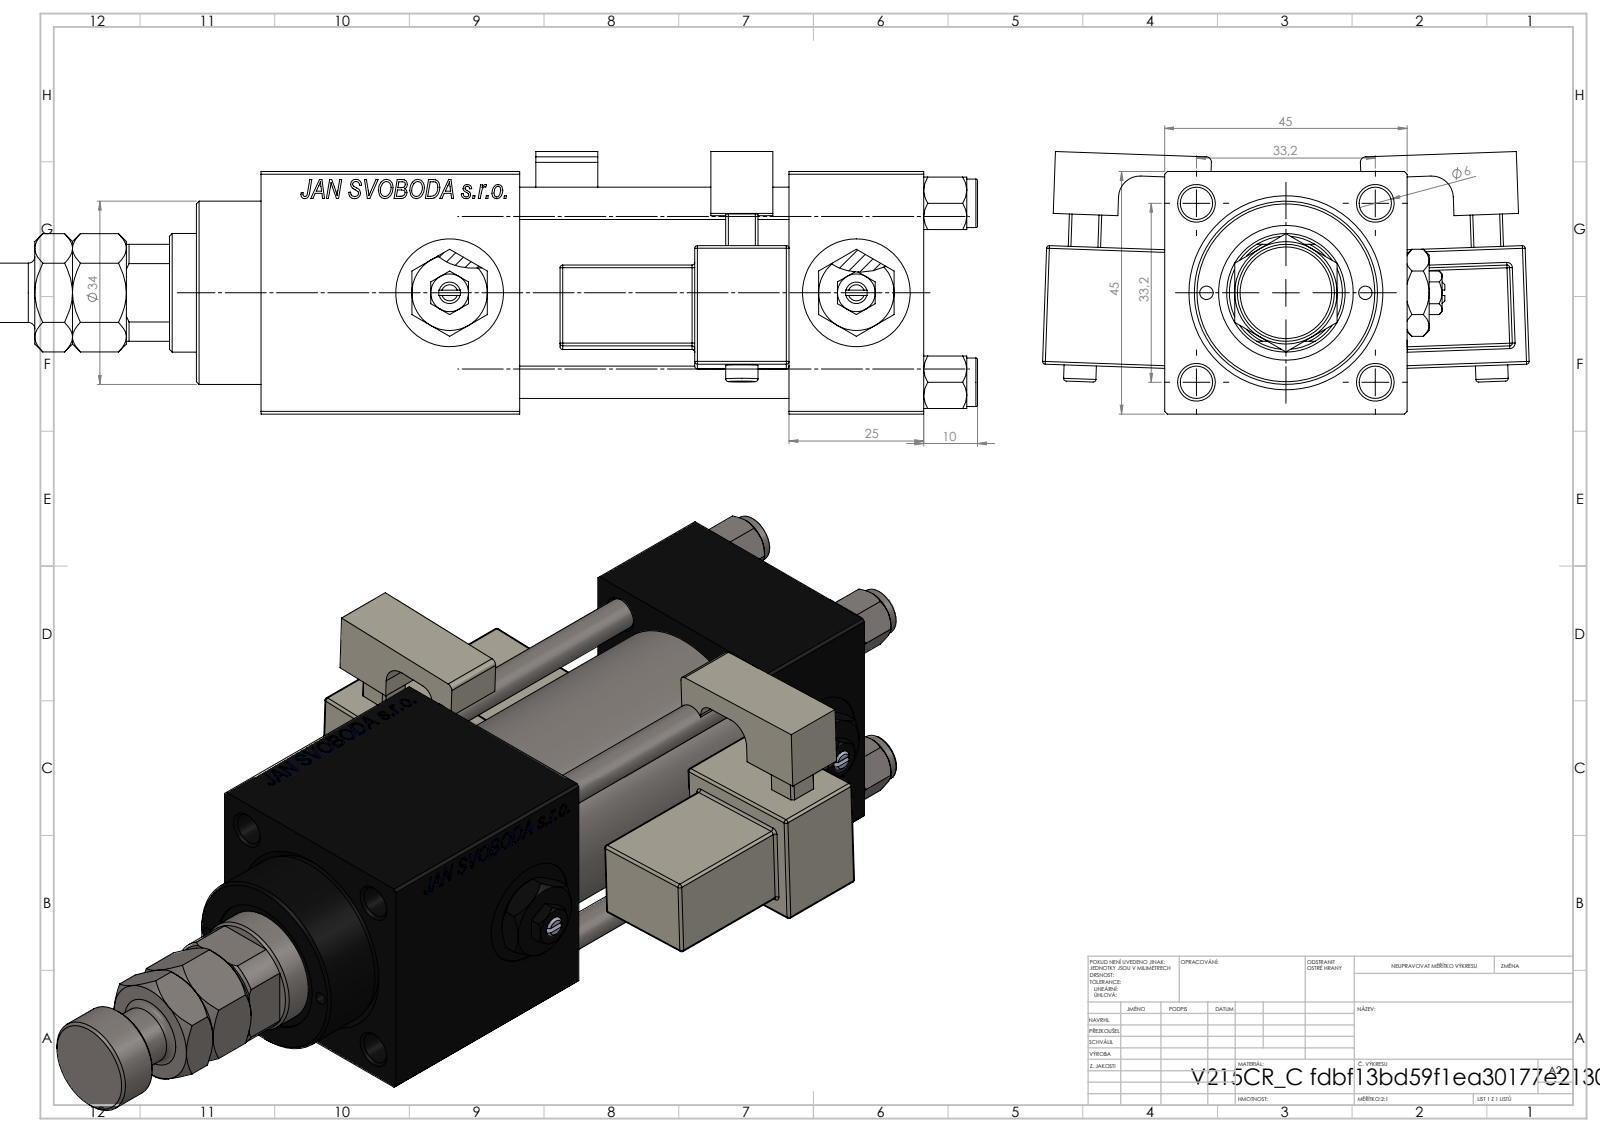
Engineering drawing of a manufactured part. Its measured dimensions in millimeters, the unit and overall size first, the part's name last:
Units: millimetres
Overall size (bounding box): 191 × 90.31 × 48.72
Round holes (diameter × count): ⌀6 ×4, ⌀2.5 ×2, ⌀7 ×2, ⌀13.16 ×2, ⌀20 ×2, ⌀10.5 ×1, ⌀22 ×1, ⌀24 ×1, ⌀25 ×1, ⌀32 ×1, ⌀33 ×1
Round bosses / shafts (diameter × count): ⌀9 ×4, ⌀6 ×2, ⌀38 ×1, ⌀34 ×1, ⌀18 ×1, ⌀11 ×1
Partial cylindrical surfaces — rounded edges, fillets, slot ends (radius × count): R0.5 ×48, R1 ×2, R2.5 ×2, R4 ×2, R10.5 ×1
Main face-to-face distances: 45, 25, 3, 50, 75, 123, 22.99, 32.5, 98, 44.8
Hole centre spacings: 16.7, 23.48, 33.2, 35.47, 14.75, 46.95, 29.5, 75.5
Volume: 256 864 mm³ · Surface area: 88 108 mm²
Bodies: 16 solids, 1464 faces (652 planar, 166 cylindrical, 646 other)
Part name (STEP PRODUCT): Zatka_pro_OIL_PORT; V215CR_VCP_C; V215CR_C_Body; NUT_M5_C (+4 more)
STEP written by: SolidWorks 2019 (CONFIG_CONTROL_DESIGN)
